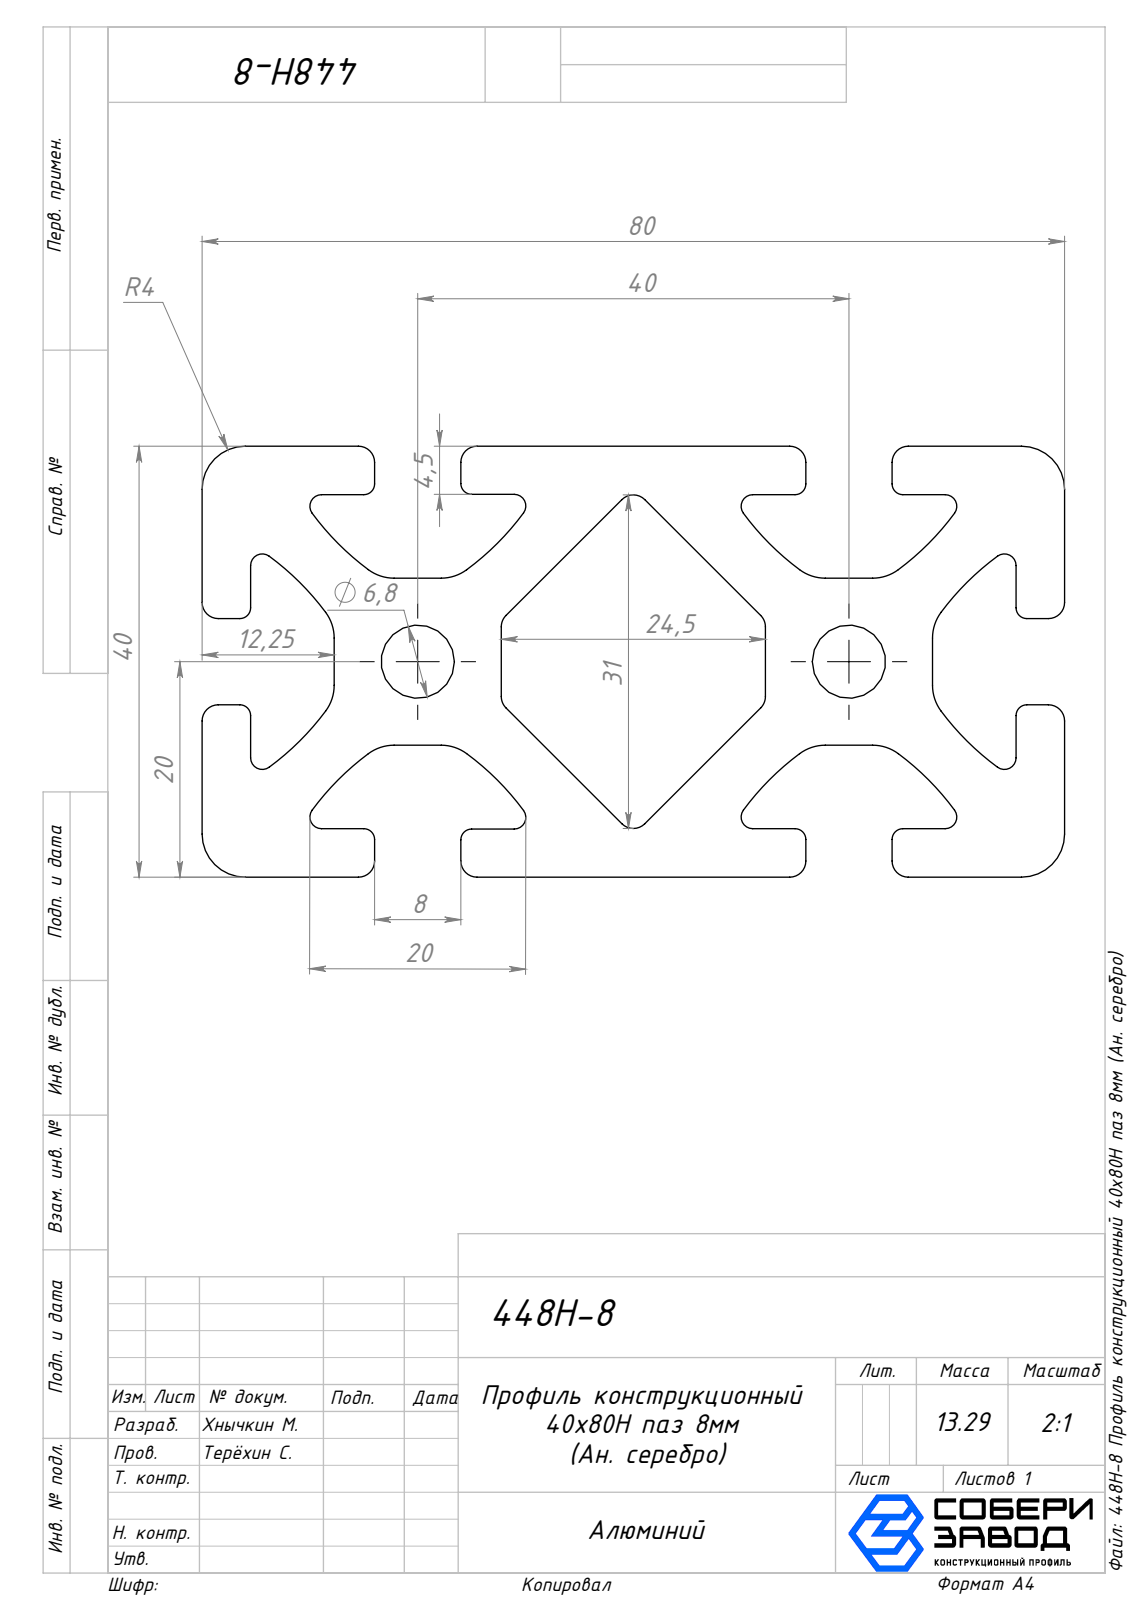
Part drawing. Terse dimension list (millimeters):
name: 448H-8 Профиль конструкционный 40х80H паз 8мм (Ан. серебро)
written by: SolidWorks 2025 (AUTOMOTIVE_DESIGN)
unit: mm
bodies: 1 solid, 126 faces (48 planar, 78 cylindrical, 0 other)
size: 1000 × 80 × 40
volume: 1 694 000 mm³; area: 589 280 mm²
holes: 2× ⌀6.8
rounds: 18× R1.5, 16× R4, 12× R1, 12× R1.08, 10× R25, 2× R24.99
face distances: 40, 4.5, 27.75, 23.25, 22.76, 12.25, 7.75, 3.75, 11.75, 35.5
hole spacings: 40
